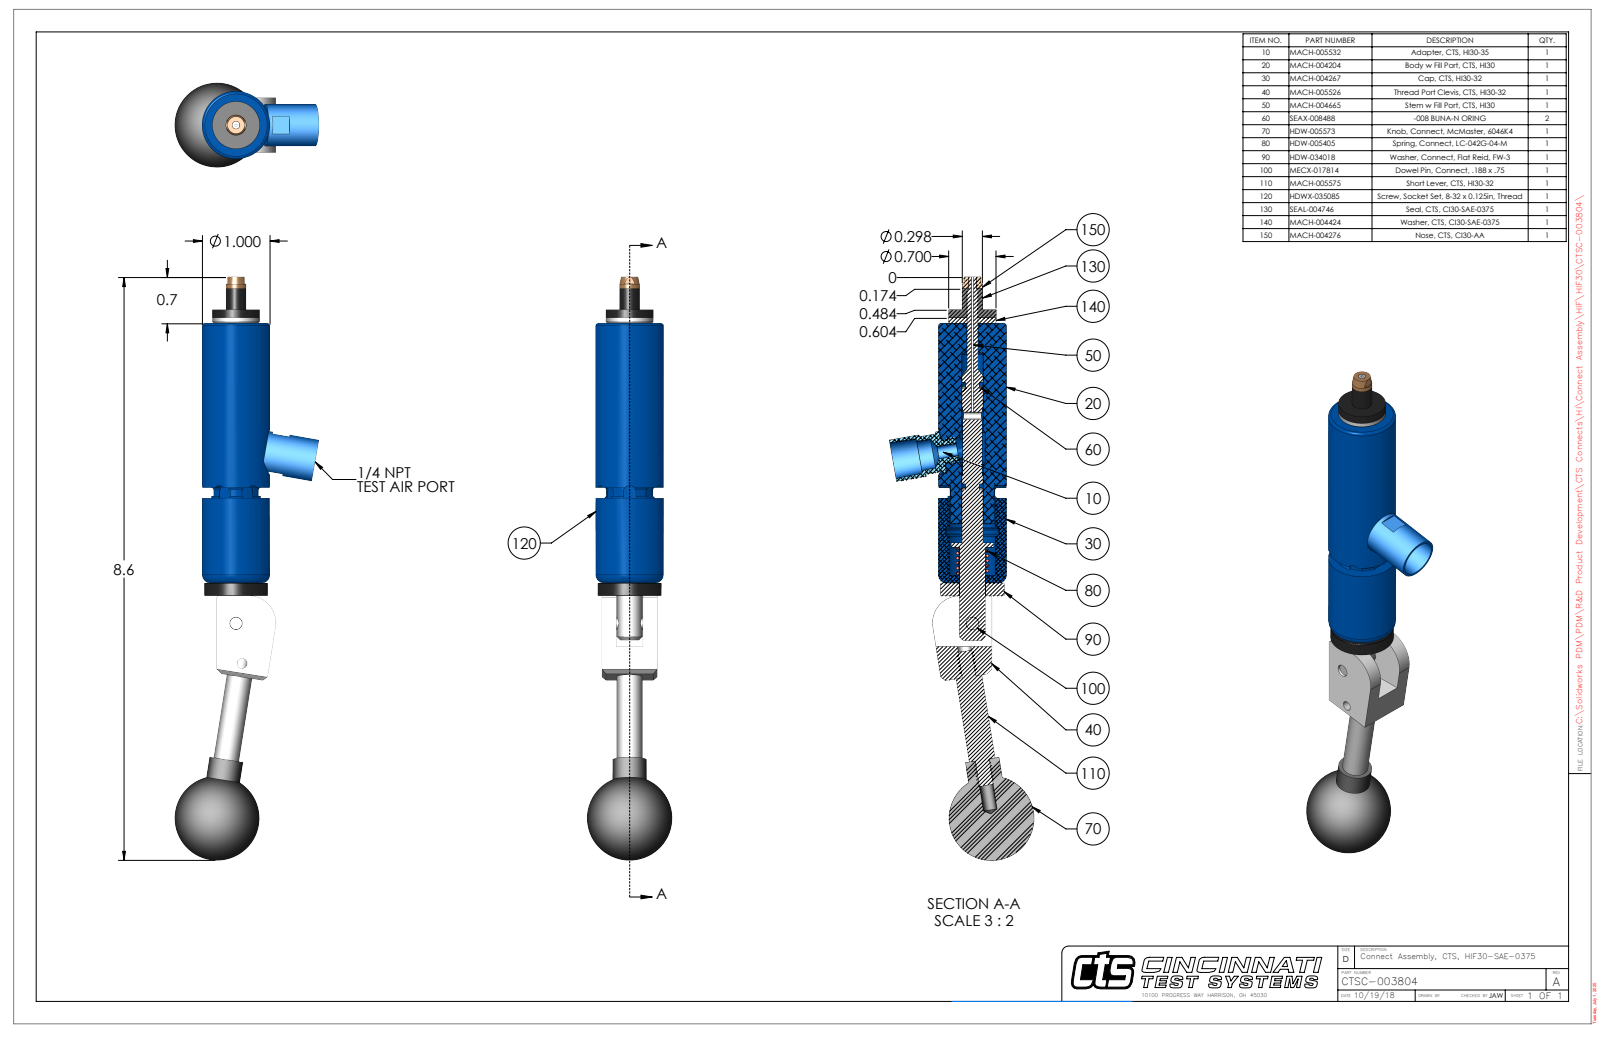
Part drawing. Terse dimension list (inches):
name: CTSC-003804
written by: SolidWorks 2023 (AUTOMOTIVE_DESIGN)
unit: in
bodies: 9 solids, 298 faces (113 planar, 123 cylindrical, 62 other)
size: 8.618 × 2.128 × 1.25
volume: 5.062 in³; area: 38.26 in²
holes: 2× ⌀0.201, 1× ⌀0.04, 1× ⌀0.082, 1× ⌀0.113, 1× ⌀0.136, 1× ⌀0.15, 1× ⌀0.155, 1× ⌀0.161, 1× ⌀0.164, 1× ⌀0.187, 1× ⌀0.189, 1× ⌀0.385
bosses: 1× ⌀1, 1× ⌀0.936, 1× ⌀0.7, 1× ⌀0.62, 1× ⌀0.5, 1× ⌀0.38, 1× ⌀0.375, 1× ⌀0.3
rounds: 6× R0.093, 1× R0.015, 1× R0.054, 1× R0.325, 1× R0.375, 1× R0.4, 1× R0.459
face distances: 0.21, 0.602, 3.837, 0.812, 4.024, 0.187, 0.08, 3.917, 4.104, 0.391
hole spacings: 0.599, 1.658, 2.252
